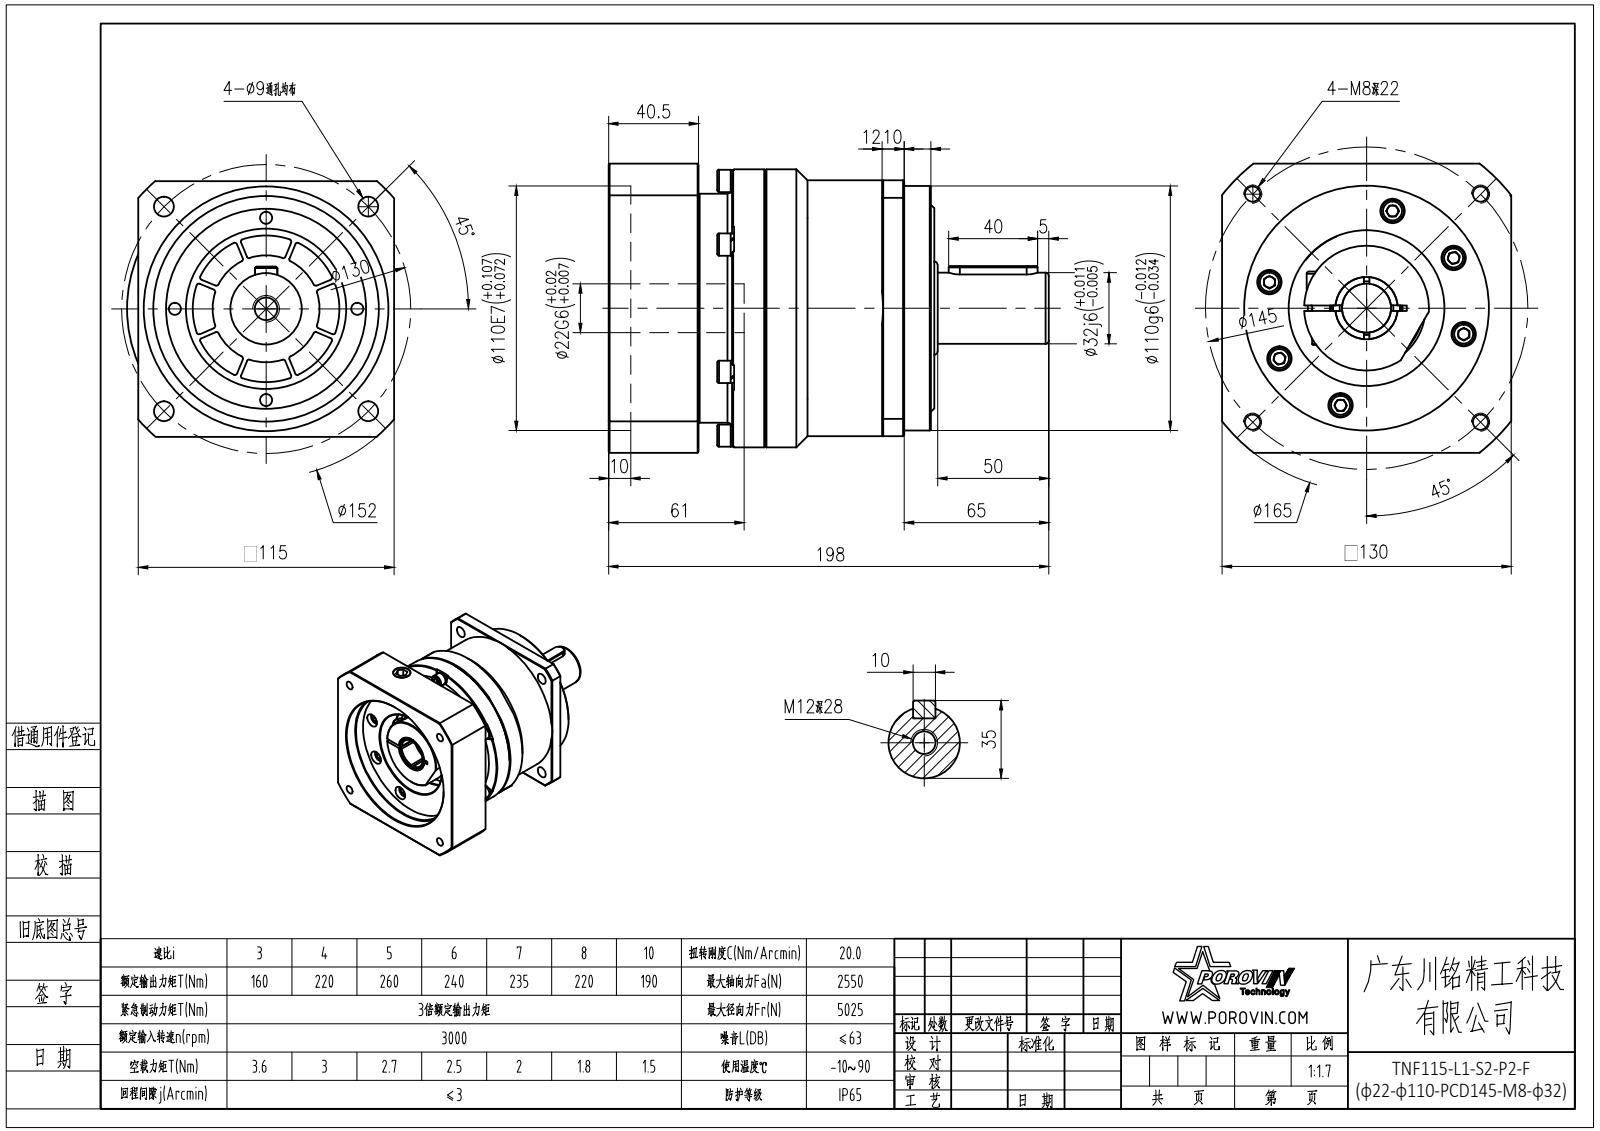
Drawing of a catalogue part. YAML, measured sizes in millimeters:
part_name: "一级齿圈加出轴 KS115 外形图; hexagon socket head cap screws gb_GB_FASTENER_SCREWS_HSHCS M6X25-N; hex socket set screws with flat point gb_GB_FASTENER_SCREWS_HSFP M16X16-N; spring lock washers--normal type gb_GB_FASTENER_WASHER_SW 6 (+2 more)"
step_written_by: "SolidWorks 2016 (CONFIG_CONTROL_DESIGN)"
units: millimeters
bodies: {solids: 33, faces: 969, planar: 413, cylindrical: 343, other: 213}
overall_size: [198, 130, 130]
volume: 1520000
surface_area: 210258
round_holes:
  - {diameter: 6.6, count: 12}
  - {diameter: 6.68, count: 12}
  - {diameter: 5, count: 6}
  - {diameter: 11, count: 6}
  - {diameter: 6.8, count: 5}
  - {diameter: 9, count: 5}
  - {diameter: 5.5, count: 4}
  - {diameter: 10.2, count: 1}
  - {diameter: 13, count: 1}
  - {diameter: 14, count: 1}
  - {diameter: 22, count: 1}
  - {diameter: 24, count: 1}
round_bosses_or_shafts:
  - {diameter: 10, count: 12}
  - {diameter: 9.88, count: 12}
  - {diameter: 6, count: 12}
  - {diameter: 125, count: 1}
  - {diameter: 115, count: 1}
  - {diameter: 103, count: 1}
  - {diameter: 56, count: 1}
  - {diameter: 48, count: 1}
partial_cylinders:
  - {radius: 1, count: 32}
  - {radius: 5.5, count: 6}
  - {radius: 5, count: 2}
  - {radius: 7, count: 1}
  - {radius: 76, count: 1}
  - {radius: 82.5, count: 1}
face_to_face_distances: [30, 130, 52.5, 40.5, 70.5, 141.5, 71, 101, 22.5, 15]
hole_center_spacings: [57.25, 46.18, 52.19, 97.37, 98.8, 105.99, 45.25, 99.16]
